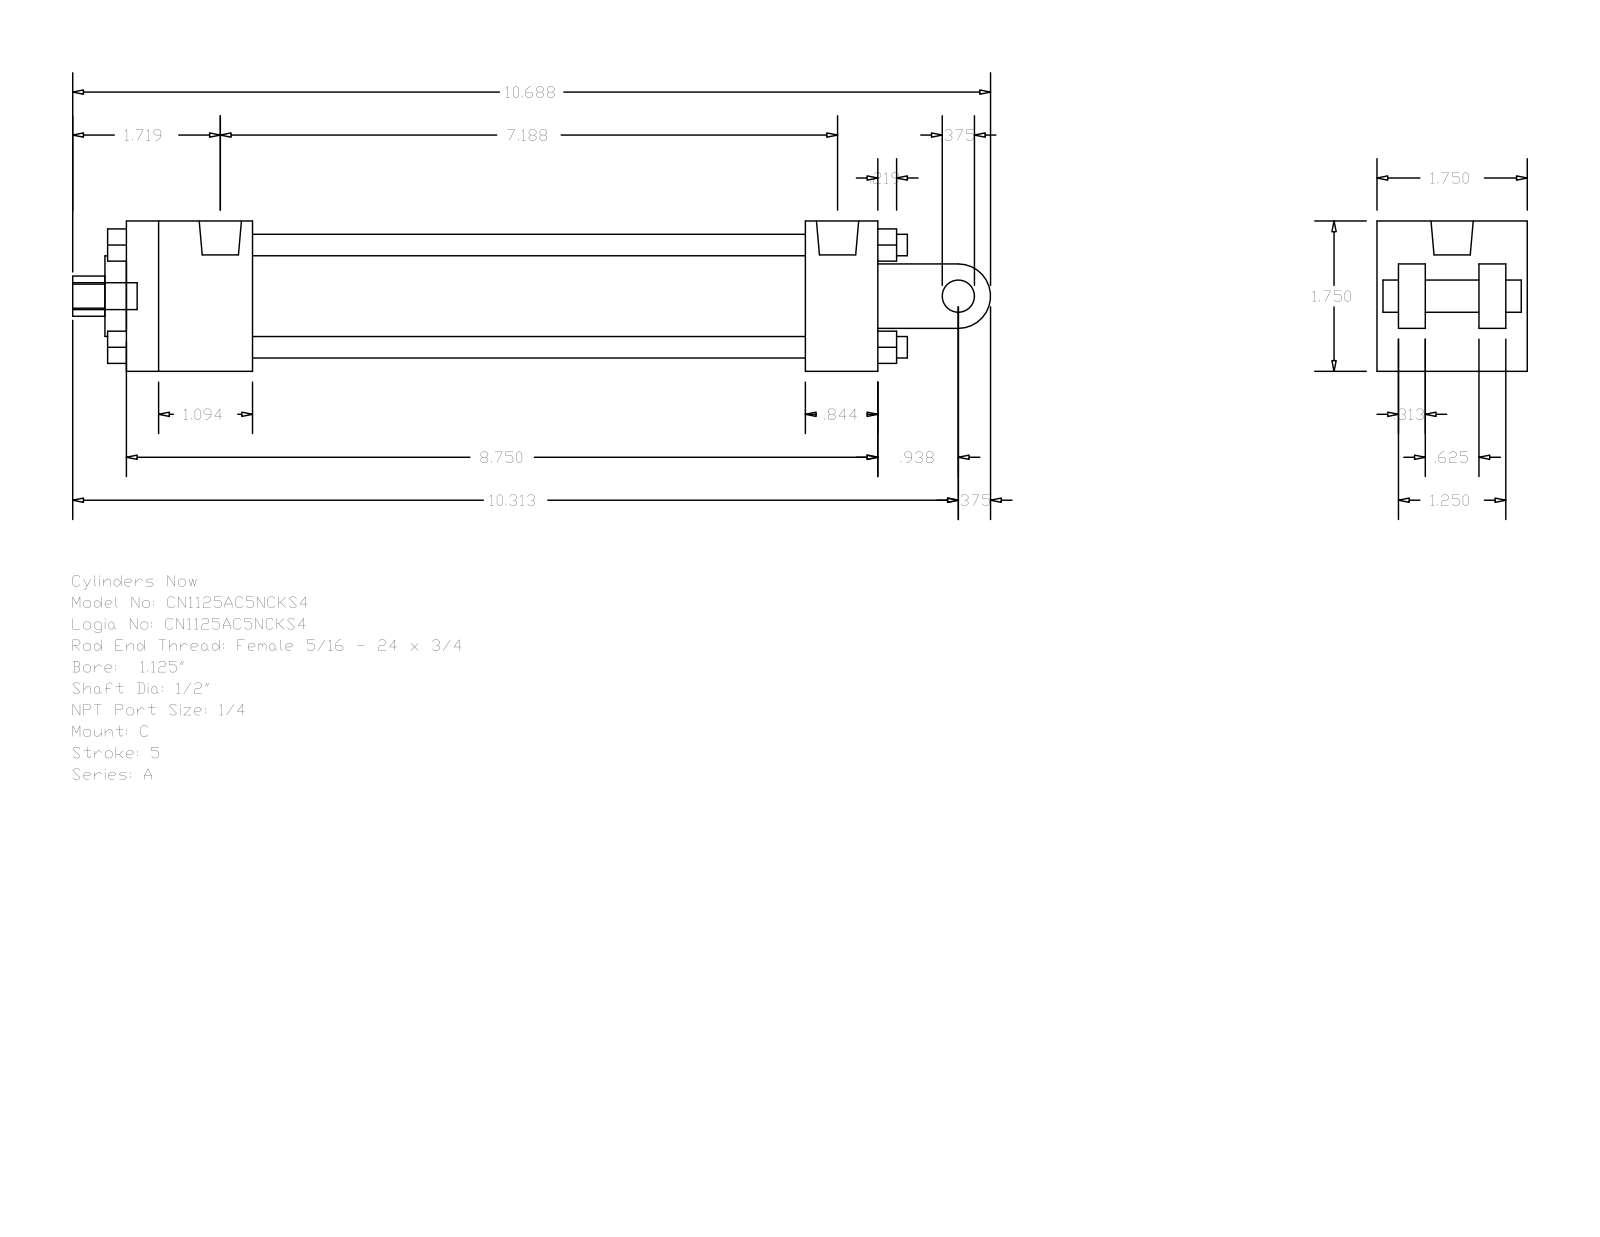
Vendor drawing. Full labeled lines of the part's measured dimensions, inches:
Part name (STEP PRODUCT): A_C__0112_0.5
STEP written by: GSSL Pune (CONFIG_CONTROL_DESIGN)
Units: inches
Bodies: 0 solids, 135 faces (102 planar, 33 cylindrical, 0 other)
Overall size (bounding box): 10.687 × 1.75 × 1.75
Round holes (diameter × count): ⌀0.219 ×2, ⌀0.492 ×1, ⌀0.5 ×1, ⌀0.937 ×1, ⌀1.255 ×1
Round bosses / shafts (diameter × count): ⌀0.25 ×4, ⌀0.219 ×2, ⌀0.492 ×1, ⌀0.375 ×1, ⌀0.313 ×1
Partial cylindrical surfaces — rounded edges, fillets, slot ends (radius × count): R0.234 ×1, R0.375 ×1
Main face-to-face distances: 1.75, 0.25, 1.25, 0.563, 8.75, 1.188, 7.906, 0.844, 1.469, 6.437
Hole centre spacings: 0.063
